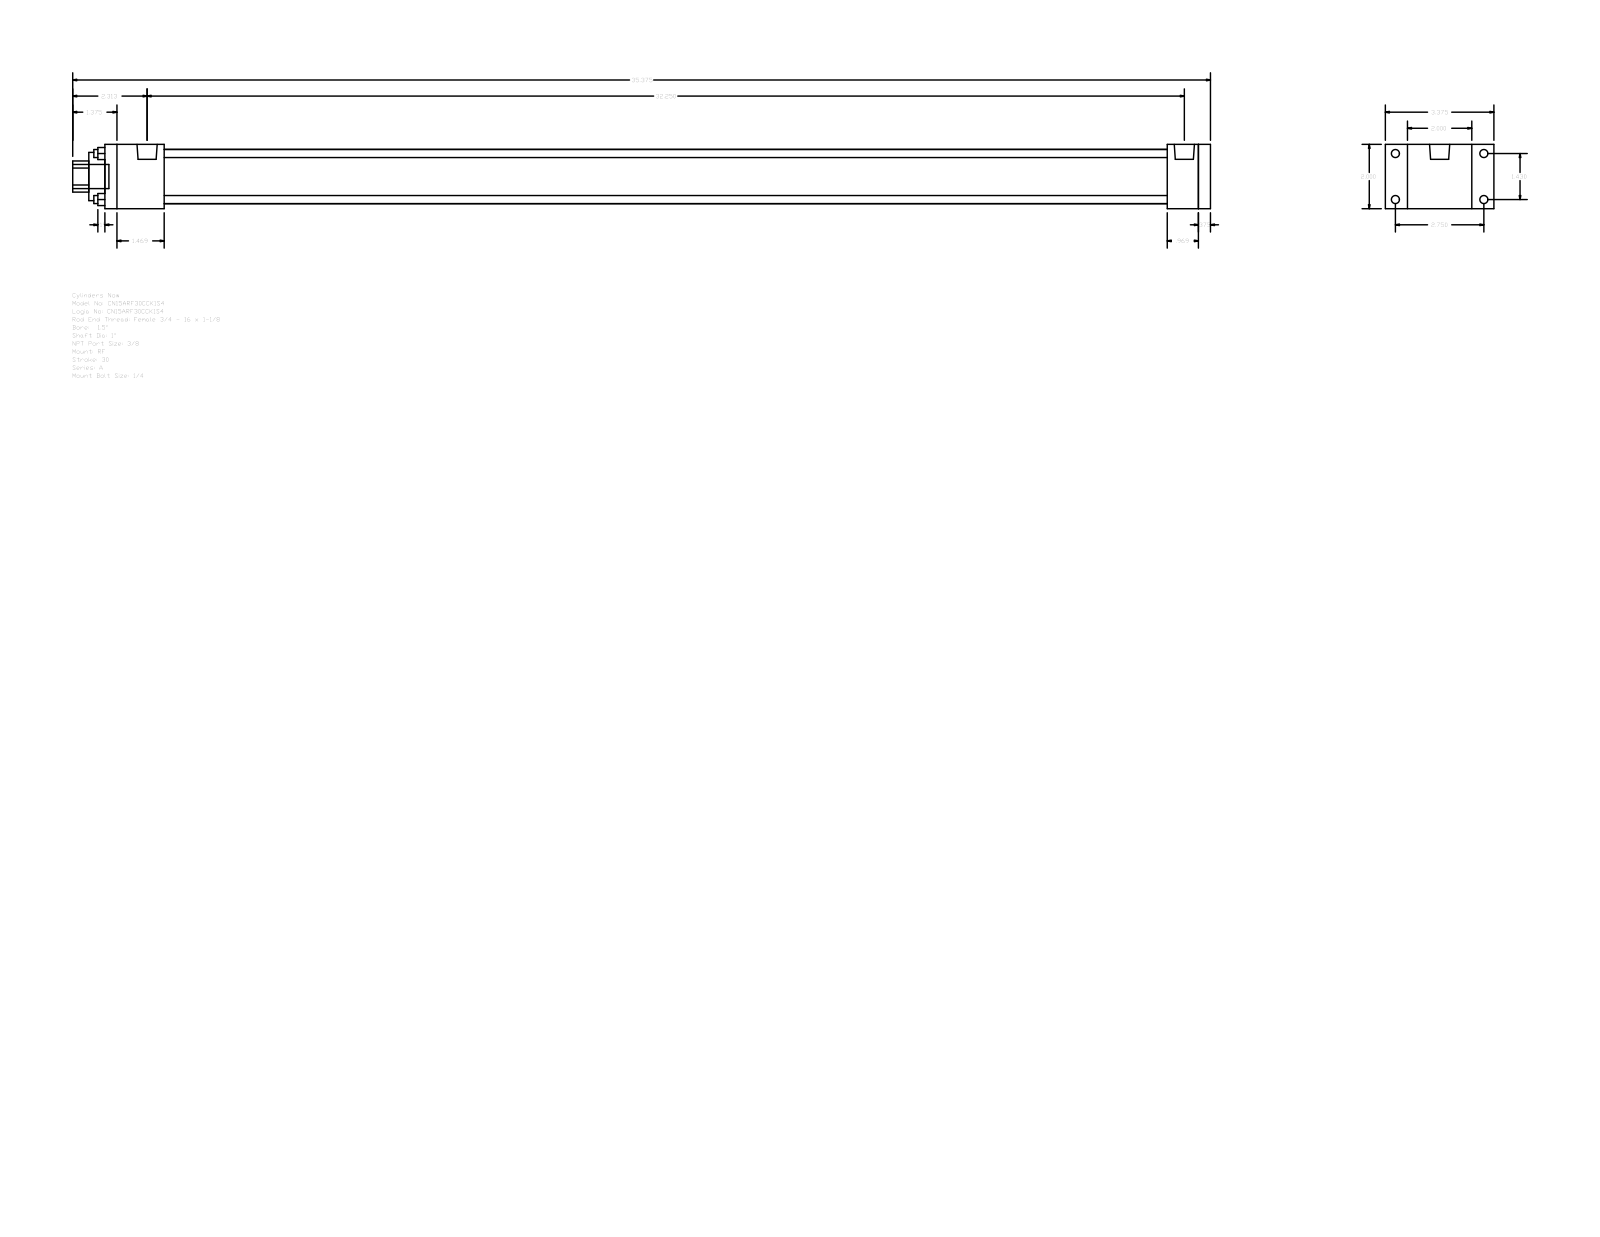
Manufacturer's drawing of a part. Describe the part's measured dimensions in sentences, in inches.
The part is named "A_RF__0150_1". Its 3-D file was written by "GSSL Pune (CONFIG_CONTROL_DESIGN)". It is 0 solids with 92 faces: 64 planar, 28 cylindrical and 0 other. Overall it measures 35.375 by 3.375 by 2 inches. Round holes: 4 of diameter 0.25, 1 of diameter 1, 1 of diameter 1.5, 1 of diameter 1.69. Round bosses or shafts: 4 of diameter 0.25, 4 of diameter 0.219, 2 of diameter 0.627, 1 of diameter 0.75. Partial cylindrical surfaces (rounded edges, fillets, slot ends): 1 of radius 0.484. The main face-to-face distances are 2, 0.375, 34, 34.375, 33.031, 0.969, 1.344, 1.844, 31.187, 32.156. The hole center spacings are 1.011, 1.43, 2.022.
